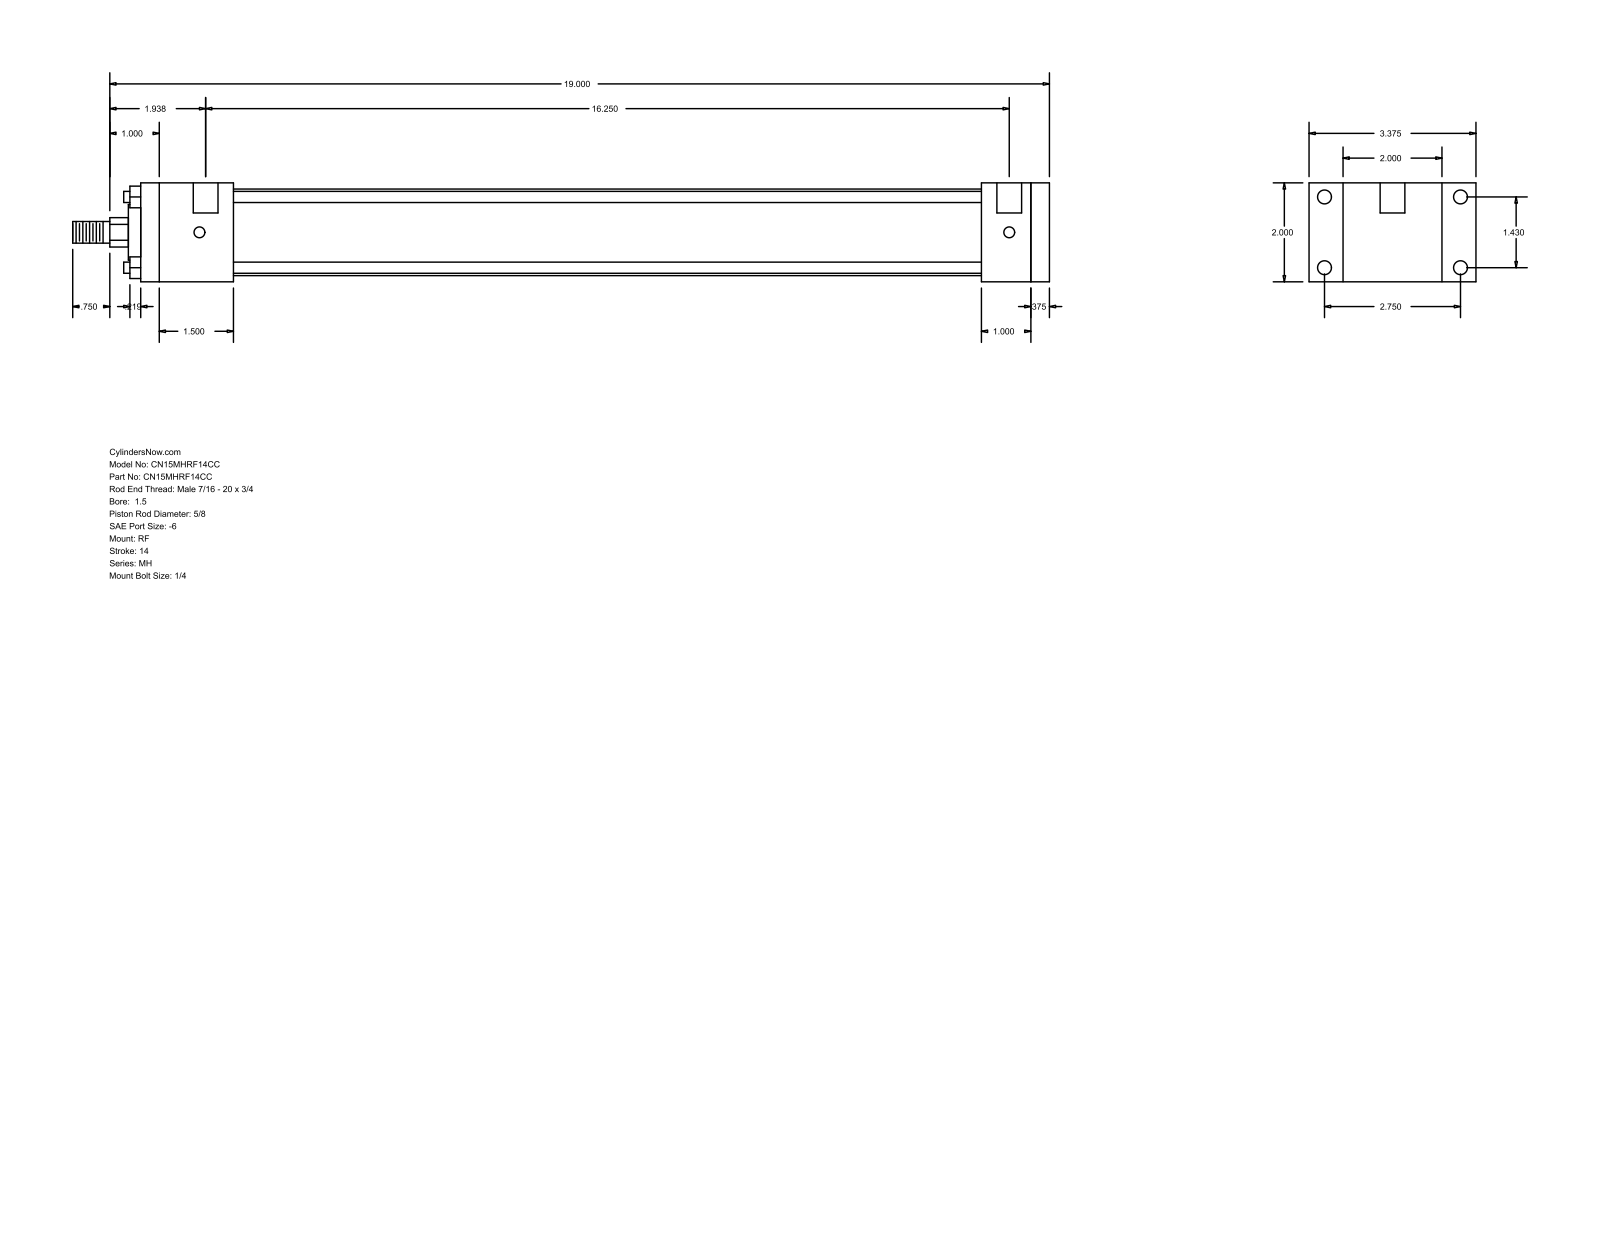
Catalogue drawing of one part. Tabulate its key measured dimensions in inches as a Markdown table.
| quantity | value |
| --- | --- |
| part name | MH_RF__0150_0.625 |
| STEP written by | GSSL Pune (CONFIG_CONTROL_DESIGN) |
| units | inches |
| bodies | 0 solids, 92 faces (64 planar, 28 cylindrical, 0 other) |
| overall size | 19.75 × 3.375 × 2 |
| round holes (diameter × count) | 0.219 × 4, 0.281 × 4, 0.5 × 2 |
| round bosses / shafts (diameter × count) | 0.225 × 4, 1.75 × 1, 1.125 × 1, 0.625 × 1, 0.437 × 1 |
| partial cylindrical surfaces (radius × count) | 0.297 × 1 |
| main face-to-face distances | 2, 0.375, 18.375, 18, 0.687, 2.687, 17, 1, 1.375, 1.875 |
| hole center spacings | 1.43, 2.75, 3.099, 16.375, 0.125, 16.25 |
